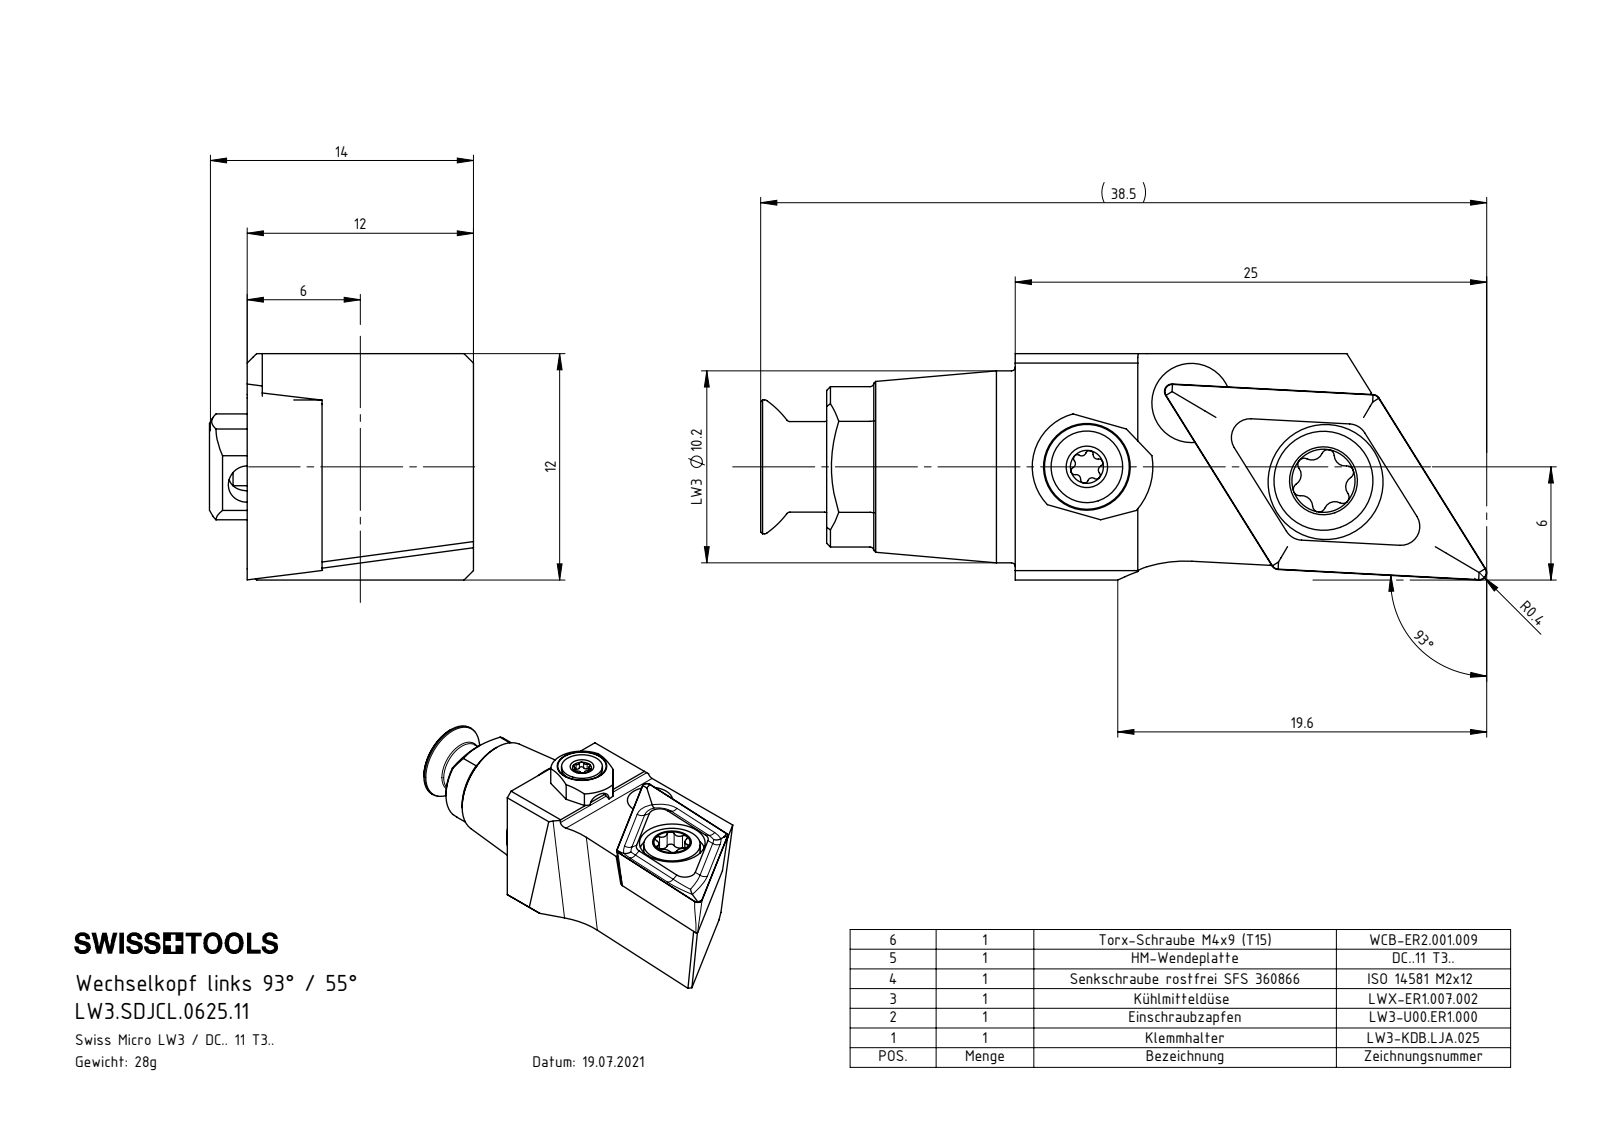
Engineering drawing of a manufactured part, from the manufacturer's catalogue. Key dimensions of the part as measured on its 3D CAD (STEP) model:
Part name (STEP PRODUCT): LW3-KDB.LJA.025_A; ISO 14581 - M2x12; WCB-ER2.001.009_A; LWX-ER1.007.002 (+3 more)
STEP written by: SolidWorks 2017 (CONFIG_CONTROL_DESIGN)
Units: millimetres
Bodies: 6 solids, 189 faces (69 planar, 52 cylindrical, 68 other)
Overall size (bounding box): 38.41 × 14 × 12
Volume: 3 255 mm³ · Surface area: 2 859 mm²
Round holes (diameter × count): ⌀1.6 ×1, ⌀2 ×1, ⌀2.5 ×1, ⌀3 ×1, ⌀3.3 ×1, ⌀4.2 ×1, ⌀4.4 ×1, ⌀5.5 ×1, ⌀6.1 ×1
Round bosses / shafts (diameter × count): ⌀10.18 ×1, ⌀6.9 ×1, ⌀6 ×1, ⌀5.25 ×1, ⌀5 ×1, ⌀4.8 ×1, ⌀4 ×1, ⌀3.8 ×1
Partial cylindrical surfaces — rounded edges, fillets, slot ends (radius × count): R0.2 ×8, R0.24 ×6, R0.34 ×6, R0.59 ×6, R0.5 ×1, R1 ×1, R2.9 ×1, R3.5 ×1
Main face-to-face distances: 12, 8.03, 3.97, 11.2, 3.17, 0.8, 2, 2.5, 13.4, 11.4
Hole centre spacings: 6.5, 8.13, 8.25, 12.57, 12.69
